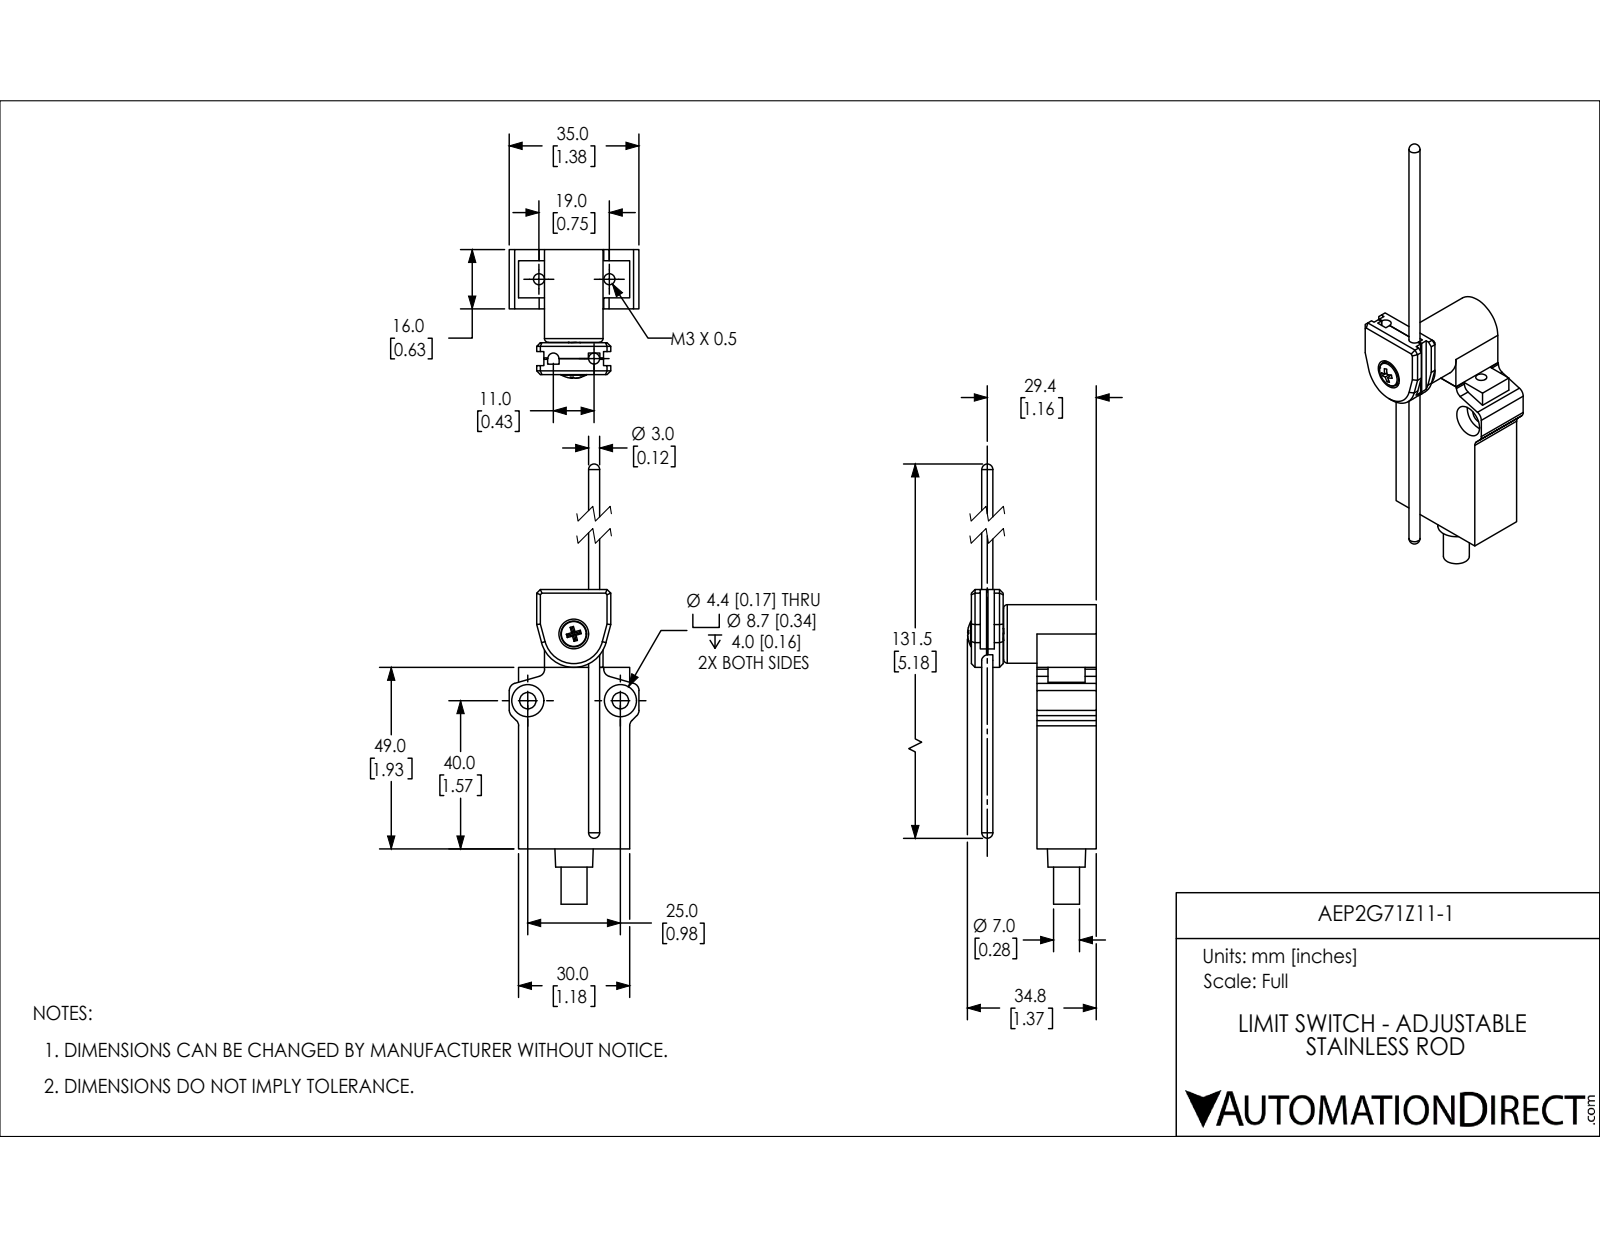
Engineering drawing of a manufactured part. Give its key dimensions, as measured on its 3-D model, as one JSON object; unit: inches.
{"part_name": "AEP2G71Z11-1", "step_written_by": "SolidWorks 2018 (AUTOMOTIVE_DESIGN)", "units": "inches", "bodies": {"solids": 6, "faces": 275, "planar": 139, "cylindrical": 114, "other": 22}, "overall_size": [5.876, 1.378, 1.366], "volume_in3": 1.933, "surface_area_in2": 19.73, "round_holes": [[0.118, 2], [0.173, 2], [0.343, 2], [0.197, 1], [0.315, 1]], "round_bosses_or_shafts": [[0.276, 2], [0.622, 1], [0.138, 1], [0.118, 1]], "partial_cylinders_radius": [[0.079, 8], [0.059, 1], [0.173, 1], [0.256, 1], [0.26, 1], [0.354, 1]], "face_to_face_distances": [0.63, 1.181, 0.169, 1.929, 0.472, 0.988, 0.098, 0.697, 0.358, 0.339], "hole_center_spacings": [0.748, 0.861, 0.865, 0.984]}
